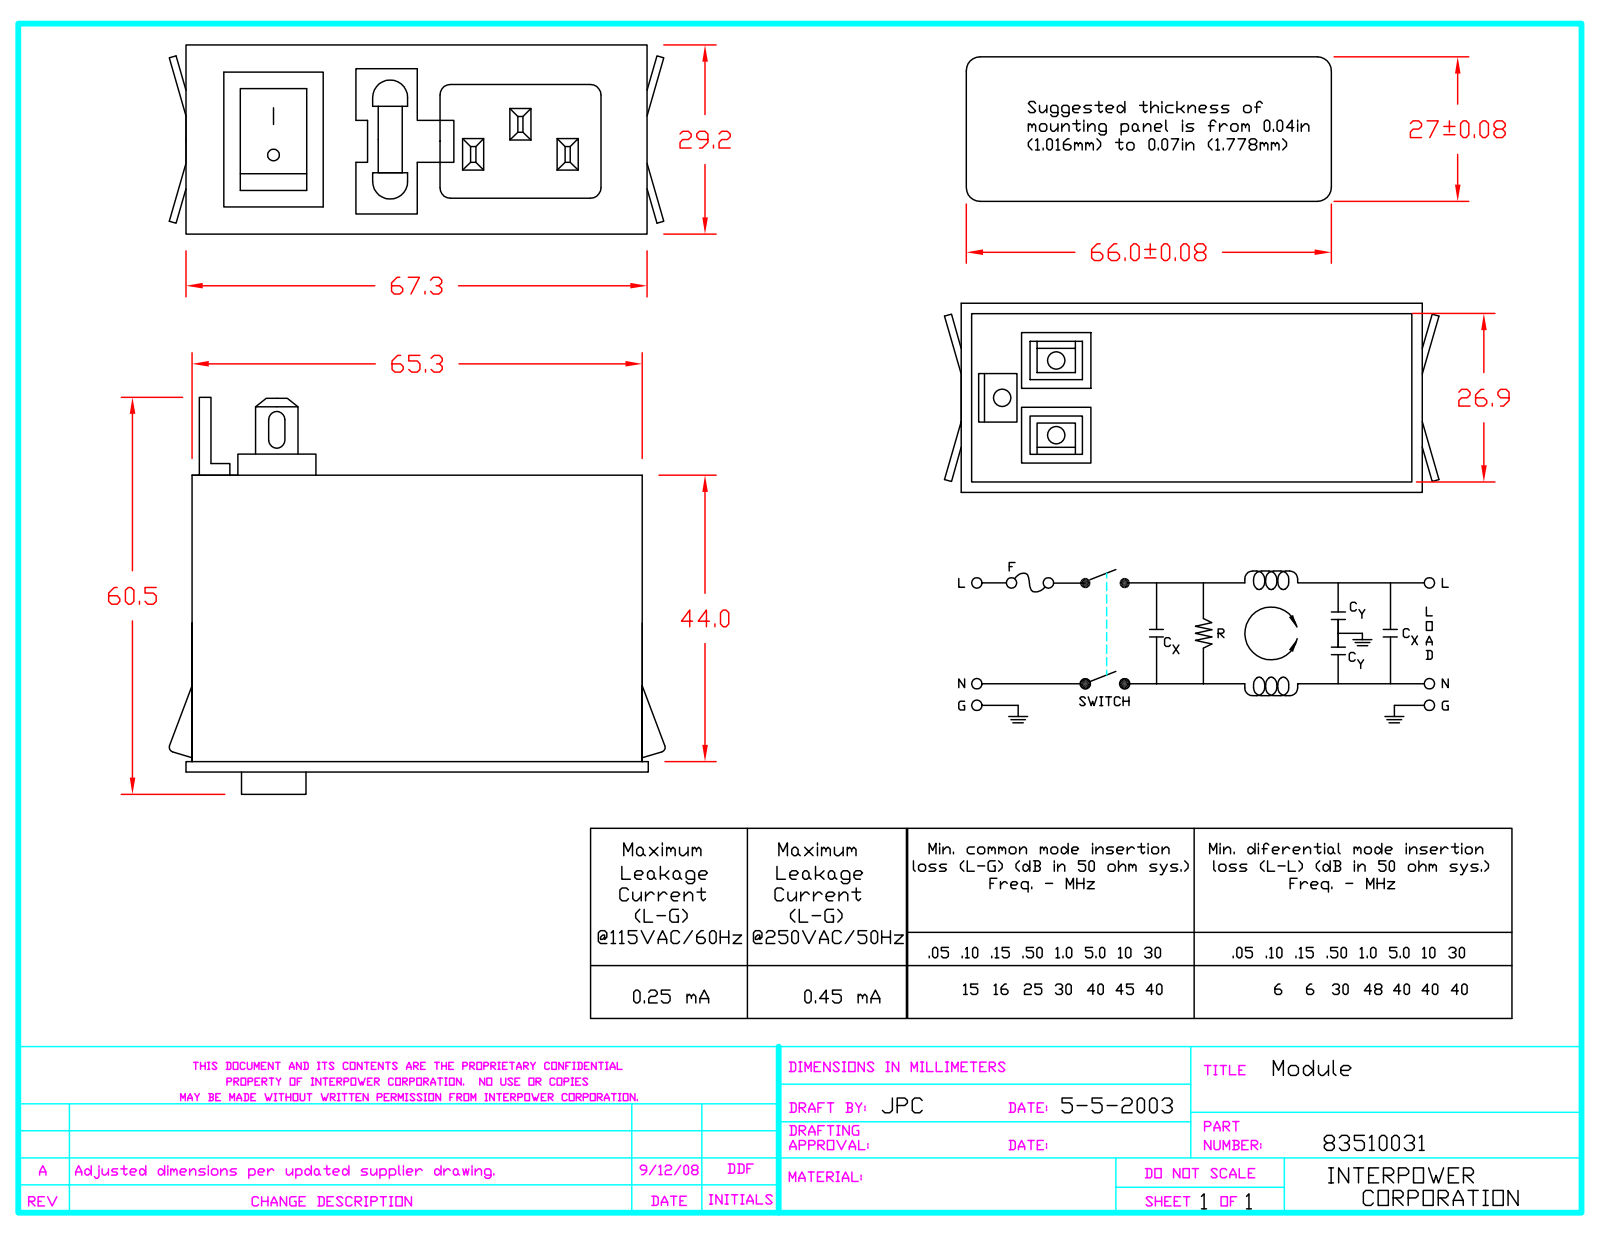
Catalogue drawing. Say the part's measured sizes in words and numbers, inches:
The part is named "83510031". Its 3-D file was written by "SolidWorks 2007 (CONFIG_CONTROL_DESIGN)". It is 1 solid with 341 faces: 237 planar, 85 cylindrical and 19 other. Overall it measures 2.9 by 2.383 by 1.15 inches. Its volume is 4.748 cubic inches and its surface area 29.52 square inches. Round holes: 2 of diameter 0.117, 1 of diameter 0.125. Round bosses or shafts: 1 of diameter 0.095. Partial cylindrical surfaces (rounded edges, fillets, slot ends): 13 of radius 0.01, 10 of radius 0.044, 8 of radius 0.015, 8 of radius 0.035, 4 of radius 0.015, 4 of radius 0.03, 4 of radius 0.041, 4 of radius 0.044. The main face-to-face distances are 1.063, 1.858, 2.567, 0.39, 0.911, 1.636, 1.331, 0.941, 1.246, 0.071.
